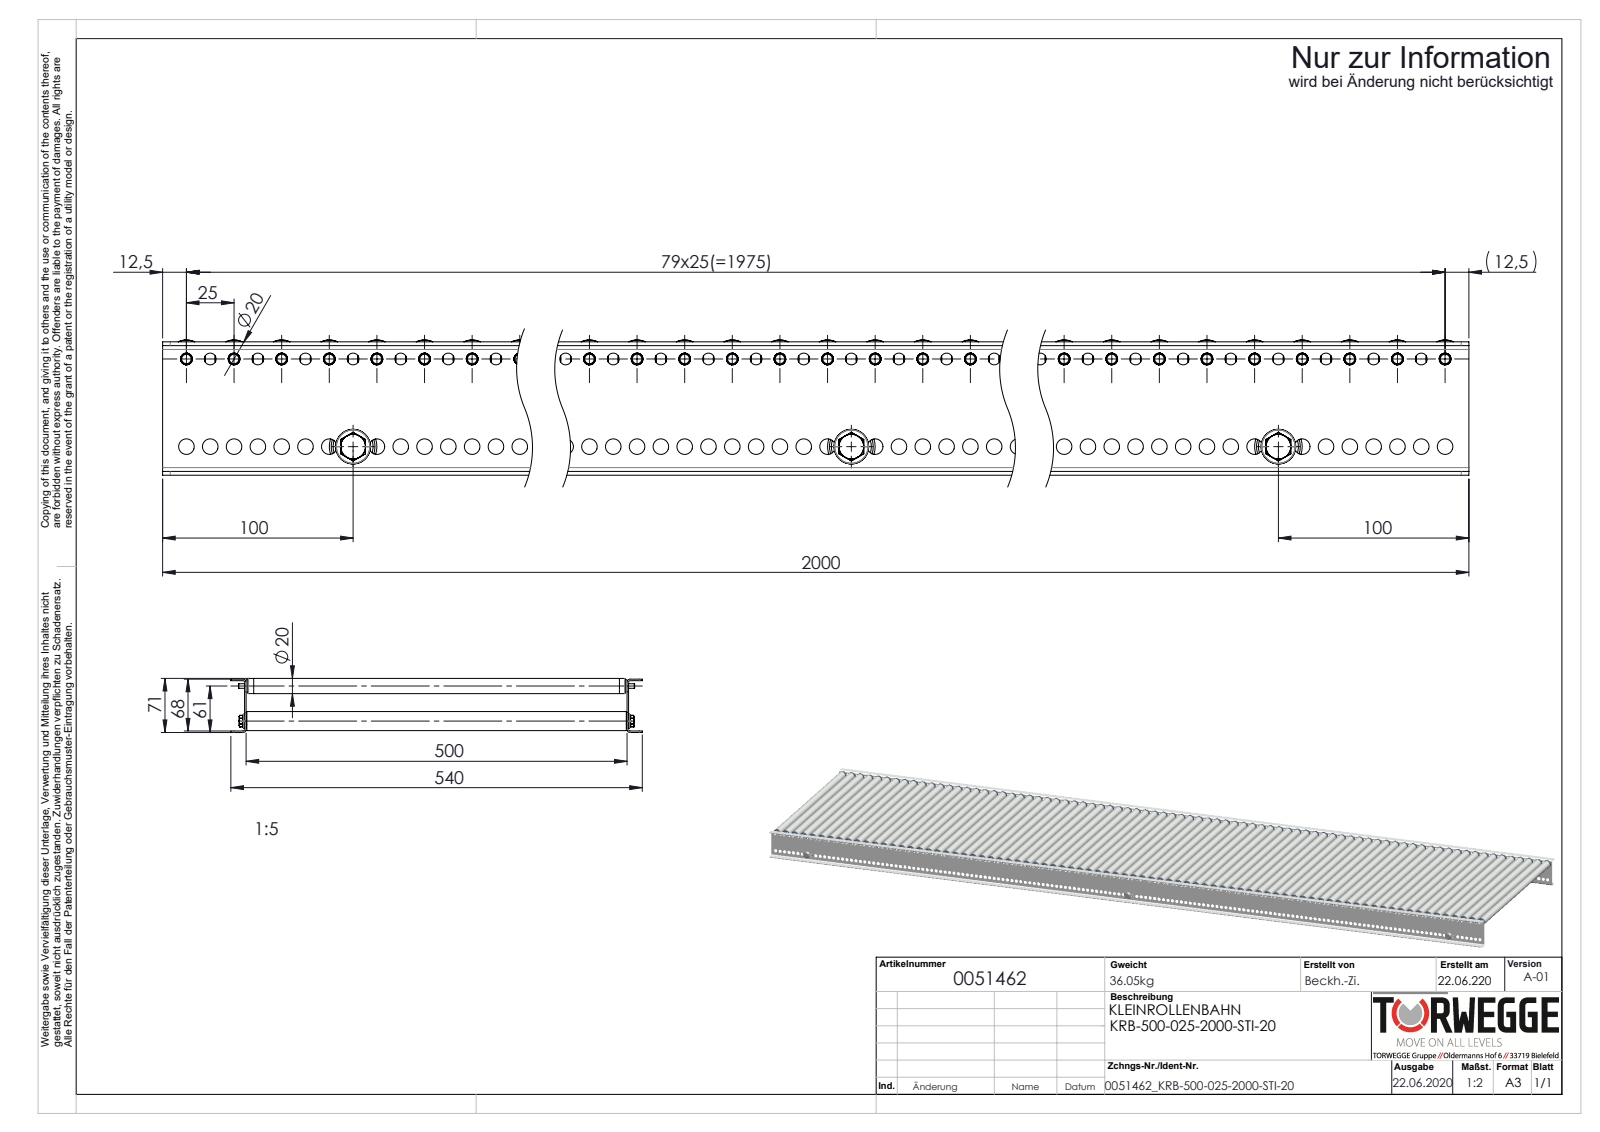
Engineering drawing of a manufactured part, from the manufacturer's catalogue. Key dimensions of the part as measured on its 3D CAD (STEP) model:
Part name (STEP PRODUCT): Traversen_KFG_L500; S100994_Sperrzahnschraube_M08x16-8.8-A2K; 0039777_Achse-Ø06-FA-KFG_L=520 fr D20; KUT50-20x1,5-STI-A6_FA-EL=KFG_S100911_KUT50-20x1-STI-A6-FA-EL=500 (+4 more)
STEP written by: SolidWorks 2020 (AUTOMOTIVE_DESIGN)
Units: millimetres
Bodies: 177 solids, 15746 faces (5122 planar, 5988 cylindrical, 4636 other)
Overall size (bounding box): 2000 × 540 × 71
Volume: 4 501 000 mm³ · Surface area: 6 948 000 mm²
Round holes (diameter × count): ⌀6.2 ×159, ⌀8.2 ×159, ⌀6.1 ×80, ⌀14.2 ×80, ⌀17.2 ×80, ⌀18 ×80, ⌀6.8 ×3, ⌀21 ×3
Round bosses / shafts (diameter × count): ⌀20 ×80, ⌀19.9 ×80, ⌀18.1 ×80, ⌀17.8 ×80, ⌀16.5 ×80, ⌀6 ×80, ⌀25 ×3, ⌀8 ×3
Partial cylindrical surfaces — rounded edges, fillets, slot ends (radius × count): R4.05 ×80, R4 ×8, R2 ×4
Main face-to-face distances: 2, 502, 68, 500, 504, 70, 66, 492, 18, 30
Hole centre spacings: 12.5, 25, 37.5, 50, 62.5, 75, 87.5, 100
